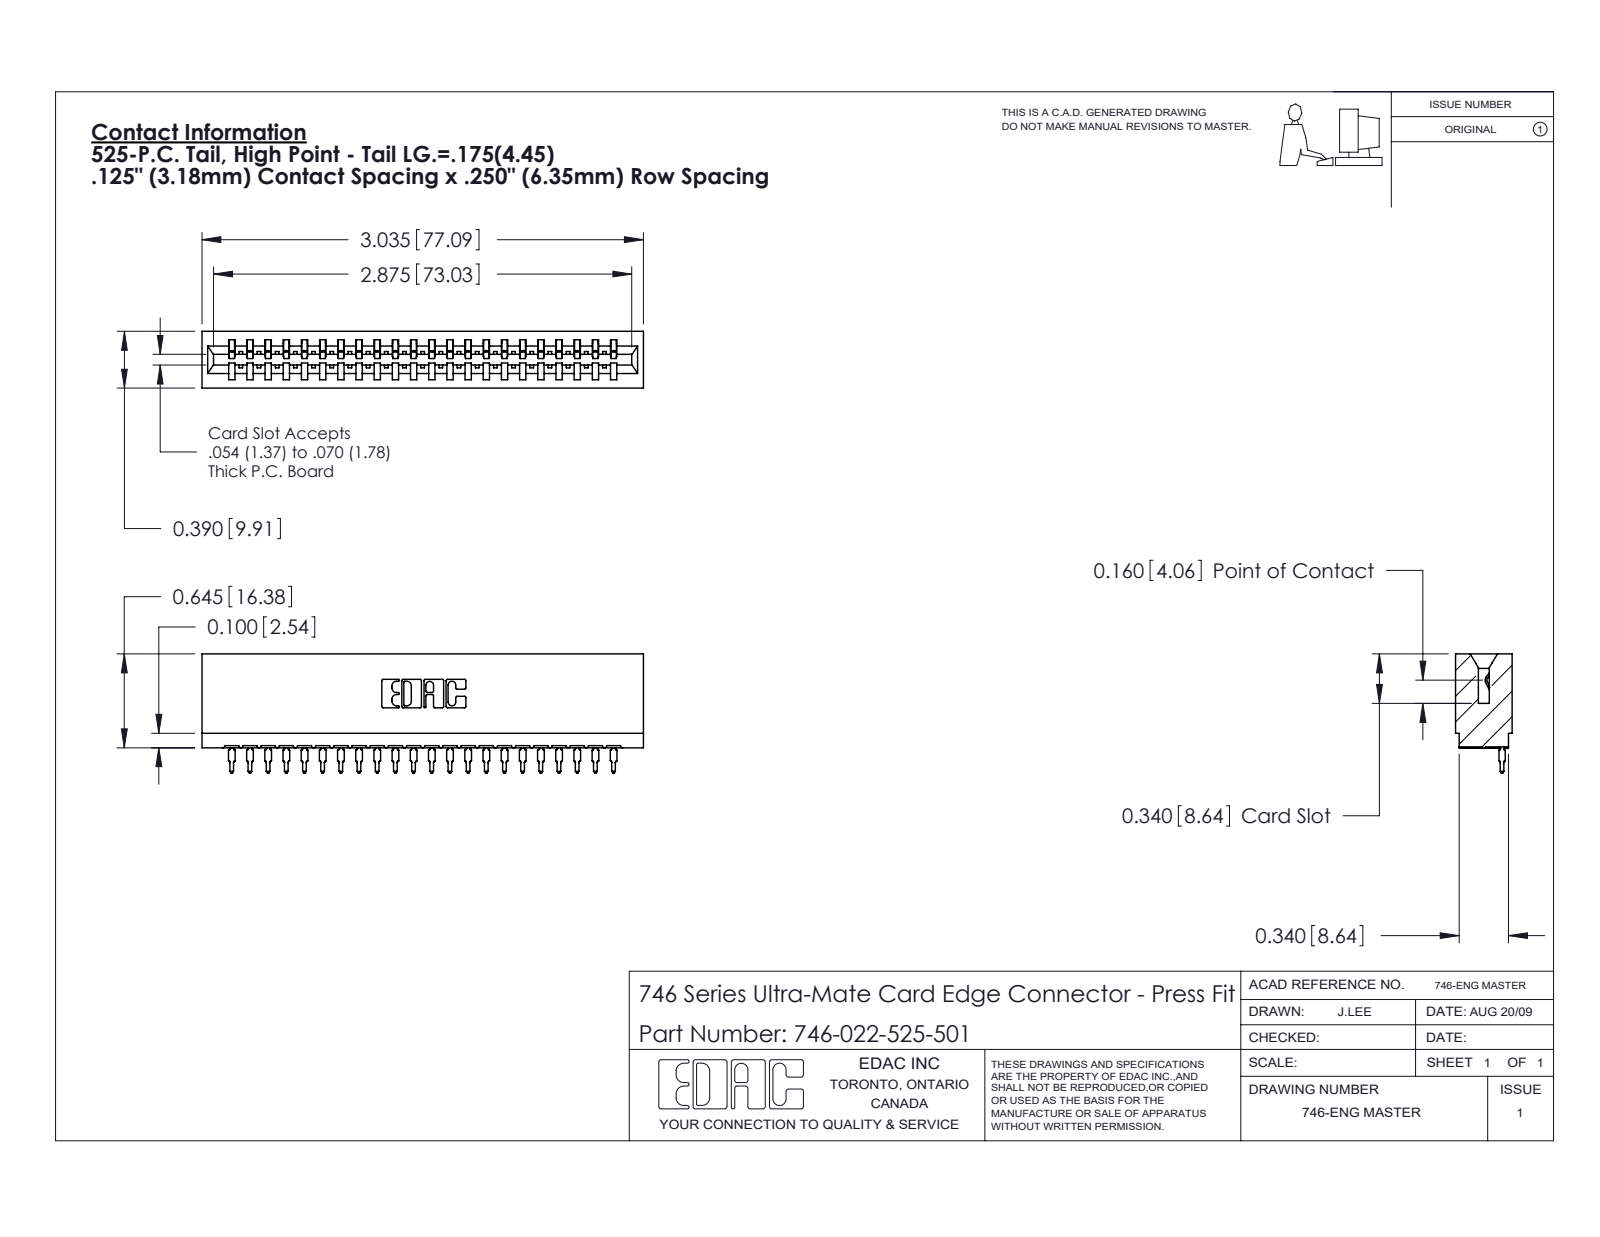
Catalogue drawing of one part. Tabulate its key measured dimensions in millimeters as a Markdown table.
| quantity | value |
| --- | --- |
| part name | 746 Part_.340 Slot Depth - 01; 746-292-001_525; 746-022-525-501 |
| STEP written by | SolidWorks 2020 (CONFIG_CONTROL_DESIGN) |
| units | millimeters |
| bodies | 23 solids, 2473 faces (1441 planar, 460 cylindrical, 572 other) |
| overall size | 77.1 × 20.8 × 9.9 |
| volume | 8 750 mm³ |
| surface area | 11 380 mm² |
| partial cylindrical surfaces (radius × count) | 0.5 × 44, 0.4 × 23, 0.3 × 22, 0.2 × 6, 0.8 × 6, 0.1 × 4, 0.3 × 4, 0.7 × 3 |
| main face-to-face distances | 1.4, 6.4, 9.9, 8.5, 0.6, 7.8, 3.2, 9.5, 3.2, 12.7 |
